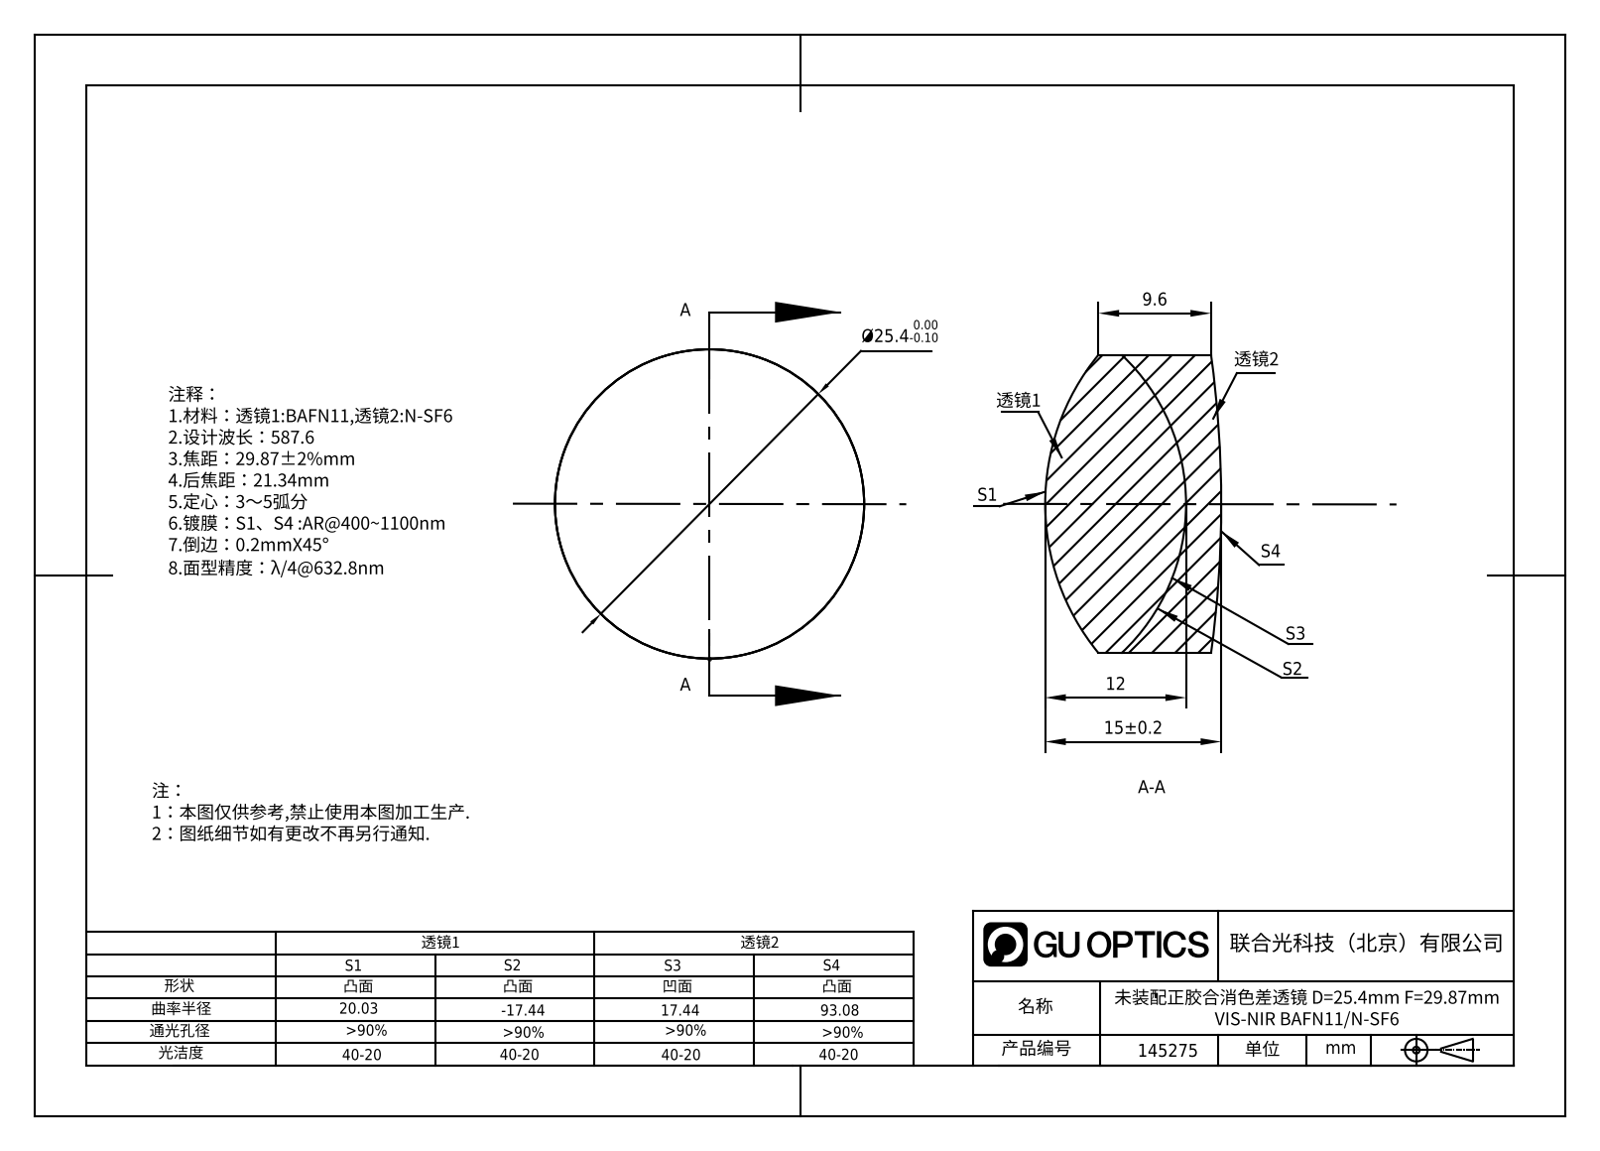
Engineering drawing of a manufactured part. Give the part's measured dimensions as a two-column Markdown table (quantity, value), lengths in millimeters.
| quantity | value |
| --- | --- |
| part name | 145275 |
| STEP written by | SolidWorks 2020 (CONFIG_CONTROL_DESIGN) |
| units | millimeters |
| bodies | 2 solids, 12 faces (0 planar, 4 cylindrical, 8 other) |
| overall size | 25.4 × 25.4 × 15 |
| volume | 6 279 mm³ |
| surface area | 3 048 mm² |
| round bosses / shafts (diameter × count) | 25.4 × 1 |
